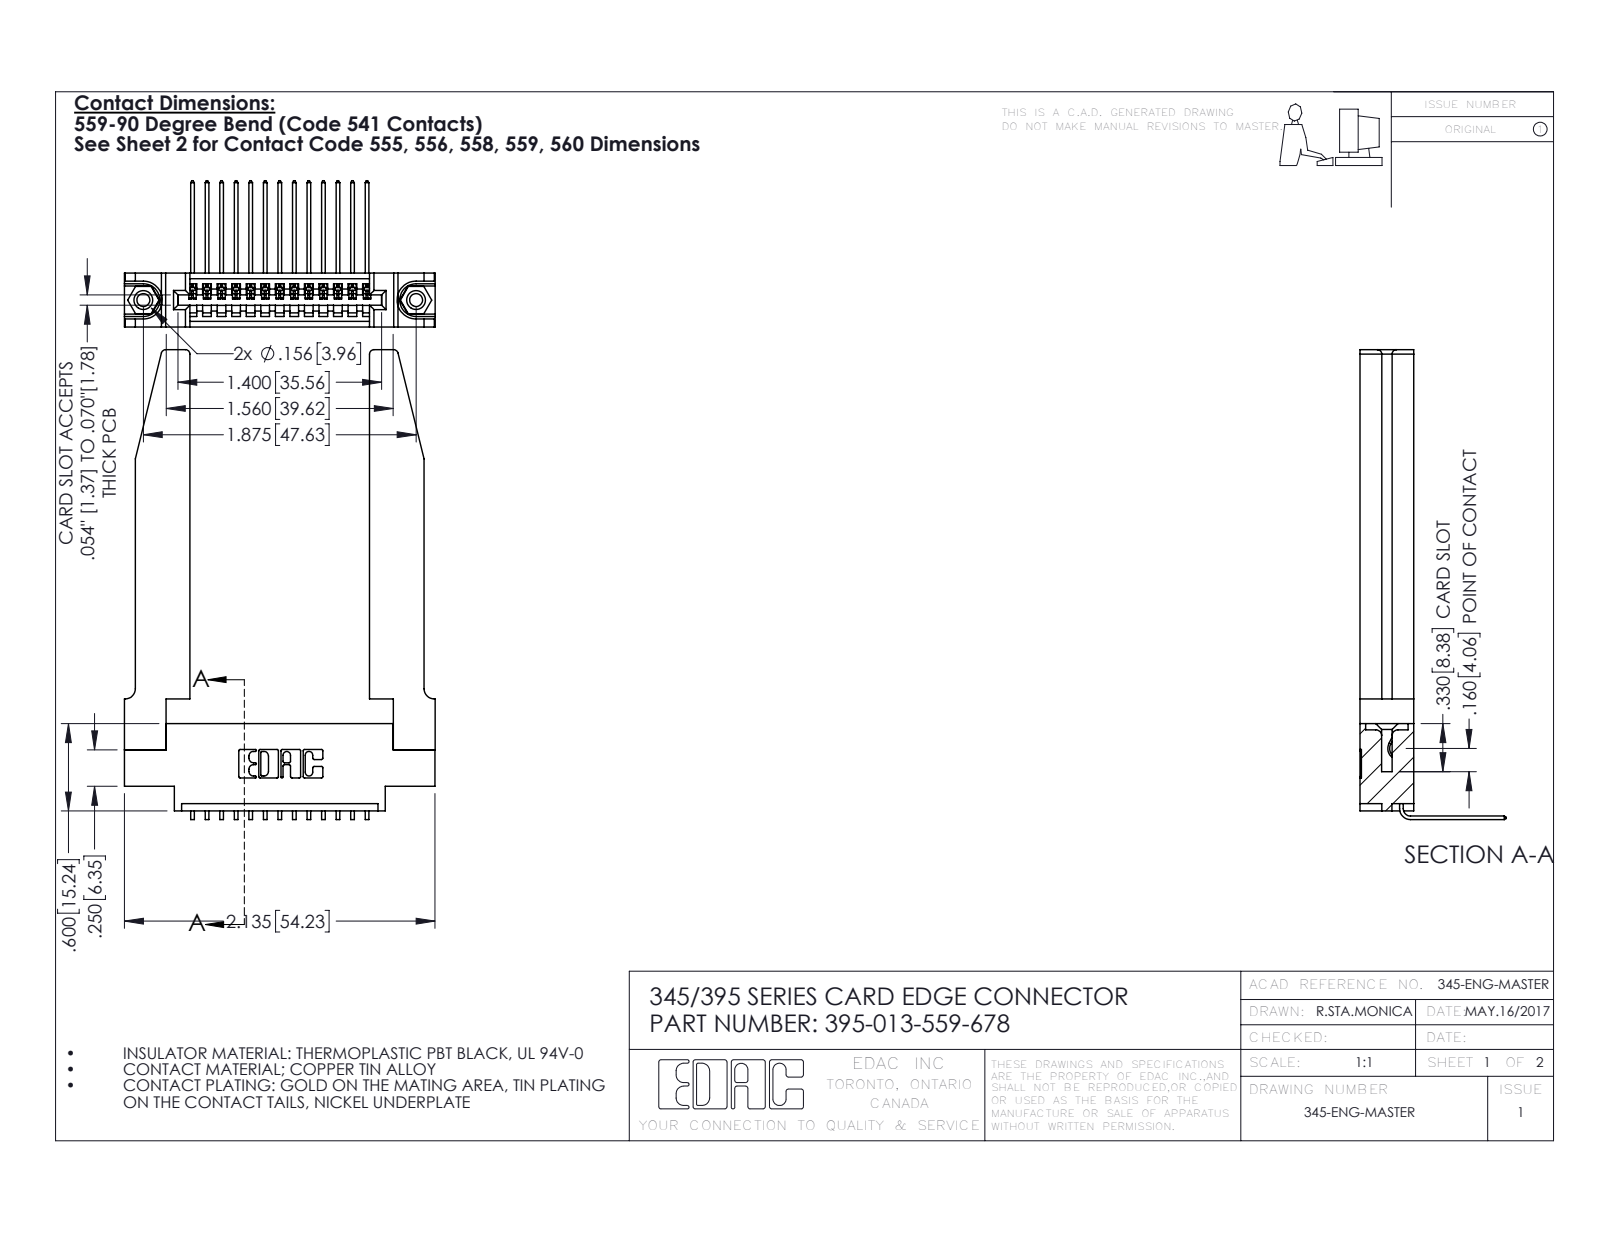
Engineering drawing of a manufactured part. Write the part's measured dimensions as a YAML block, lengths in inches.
part_name: "345 Part_0.170 Offset - 0.156 Dia-TH; 345-292-001_558 559 Tail - 1; 345-250-001_345-250-001-102; 345-220-078_345-220-078 (+1 more)"
step_written_by: "SolidWorks 2016 (CONFIG_CONTROL_DESIGN)"
units: inches
bodies: {solids: 18, faces: 1144, planar: 772, cylindrical: 320, other: 52}
overall_size: [3.229, 2.136, 1.005]
volume: 0.77
surface_area: 20.57
round_holes:
  - {diameter: 0.089, count: 2}
  - {diameter: 0.125, count: 2}
  - {diameter: 0.156, count: 2}
  - {diameter: 0.064, count: 1}
round_bosses_or_shafts:
  - {diameter: 0.155, count: 2}
partial_cylinders:
  - {radius: 0.006, count: 26}
  - {radius: 0.01, count: 22}
  - {radius: 0.03, count: 8}
  - {radius: 0.007, count: 6}
  - {radius: 0.031, count: 6}
  - {radius: 0.026, count: 3}
  - {radius: 0.031, count: 2}
  - {radius: 0.04, count: 2}
face_to_face_distances: [0.37, 0.072, 0.298, 0.148, 0.15, 0.22, 0.077, 1.235, 0.123, 0.098]
hole_center_spacings: [0.27, 1.643, 1.875]
